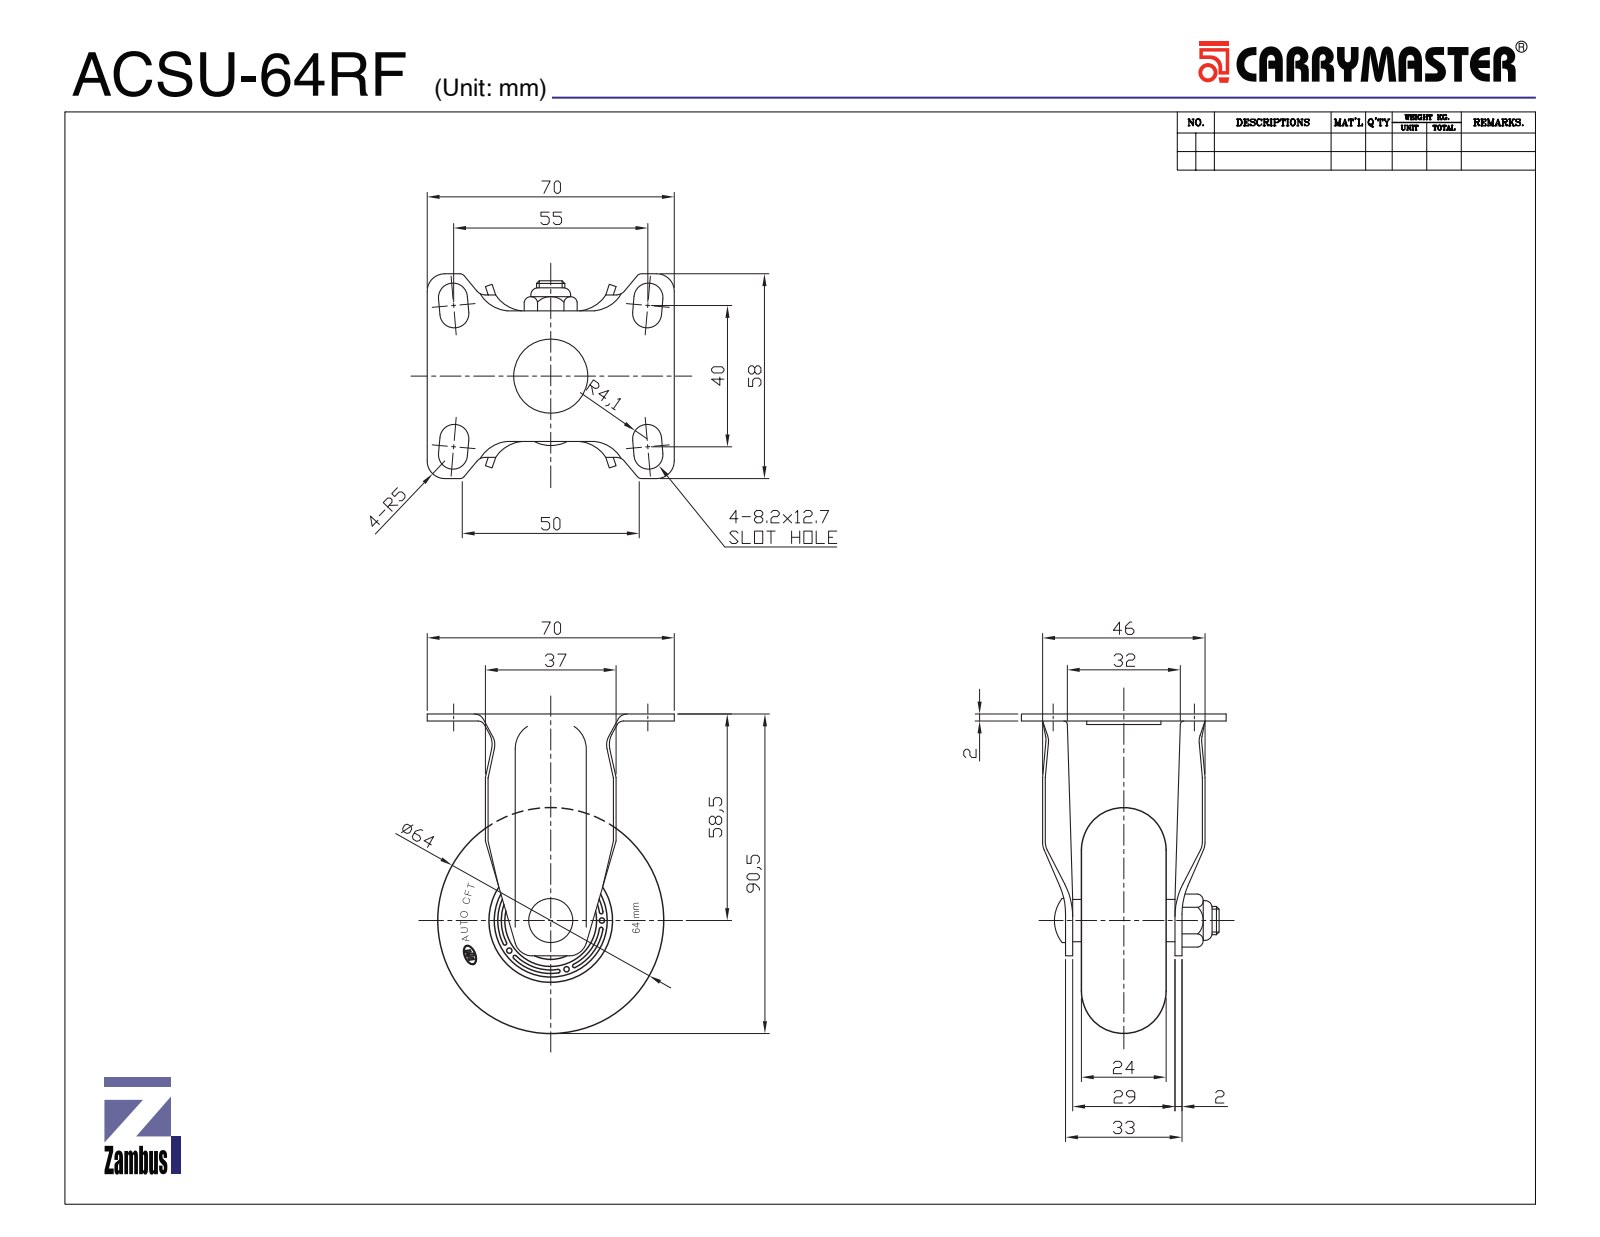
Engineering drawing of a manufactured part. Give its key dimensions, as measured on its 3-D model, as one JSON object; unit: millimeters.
{"part_name": "ACSU-64RF", "step_written_by": "SolidWorks 2015 (CONFIG_CONTROL_DESIGN)", "units": "millimeters", "bodies": {"solids": 9, "faces": 470, "planar": 155, "cylindrical": 200, "other": 115}, "overall_size": [90, 70, 57.8], "volume_mm3": 79911, "surface_area_mm2": 48201, "round_holes": [[6.8, 1], [8, 1], [12.67, 1], [17.33, 1], [18.5, 1], [22, 1], [35, 1]], "round_bosses_or_shafts": [[12.5, 1], [11.8, 1], [7.85, 1]], "partial_cylinders_radius": [[1, 58], [1.5, 10], [2, 10], [8, 9], [4.1, 8], [0.5, 6], [5, 6], [10, 4]], "face_to_face_distances": [2, 35.08, 1, 6.54, 30.54, 4.54, 28.54, 37.08, 33.08, 3.5]}
